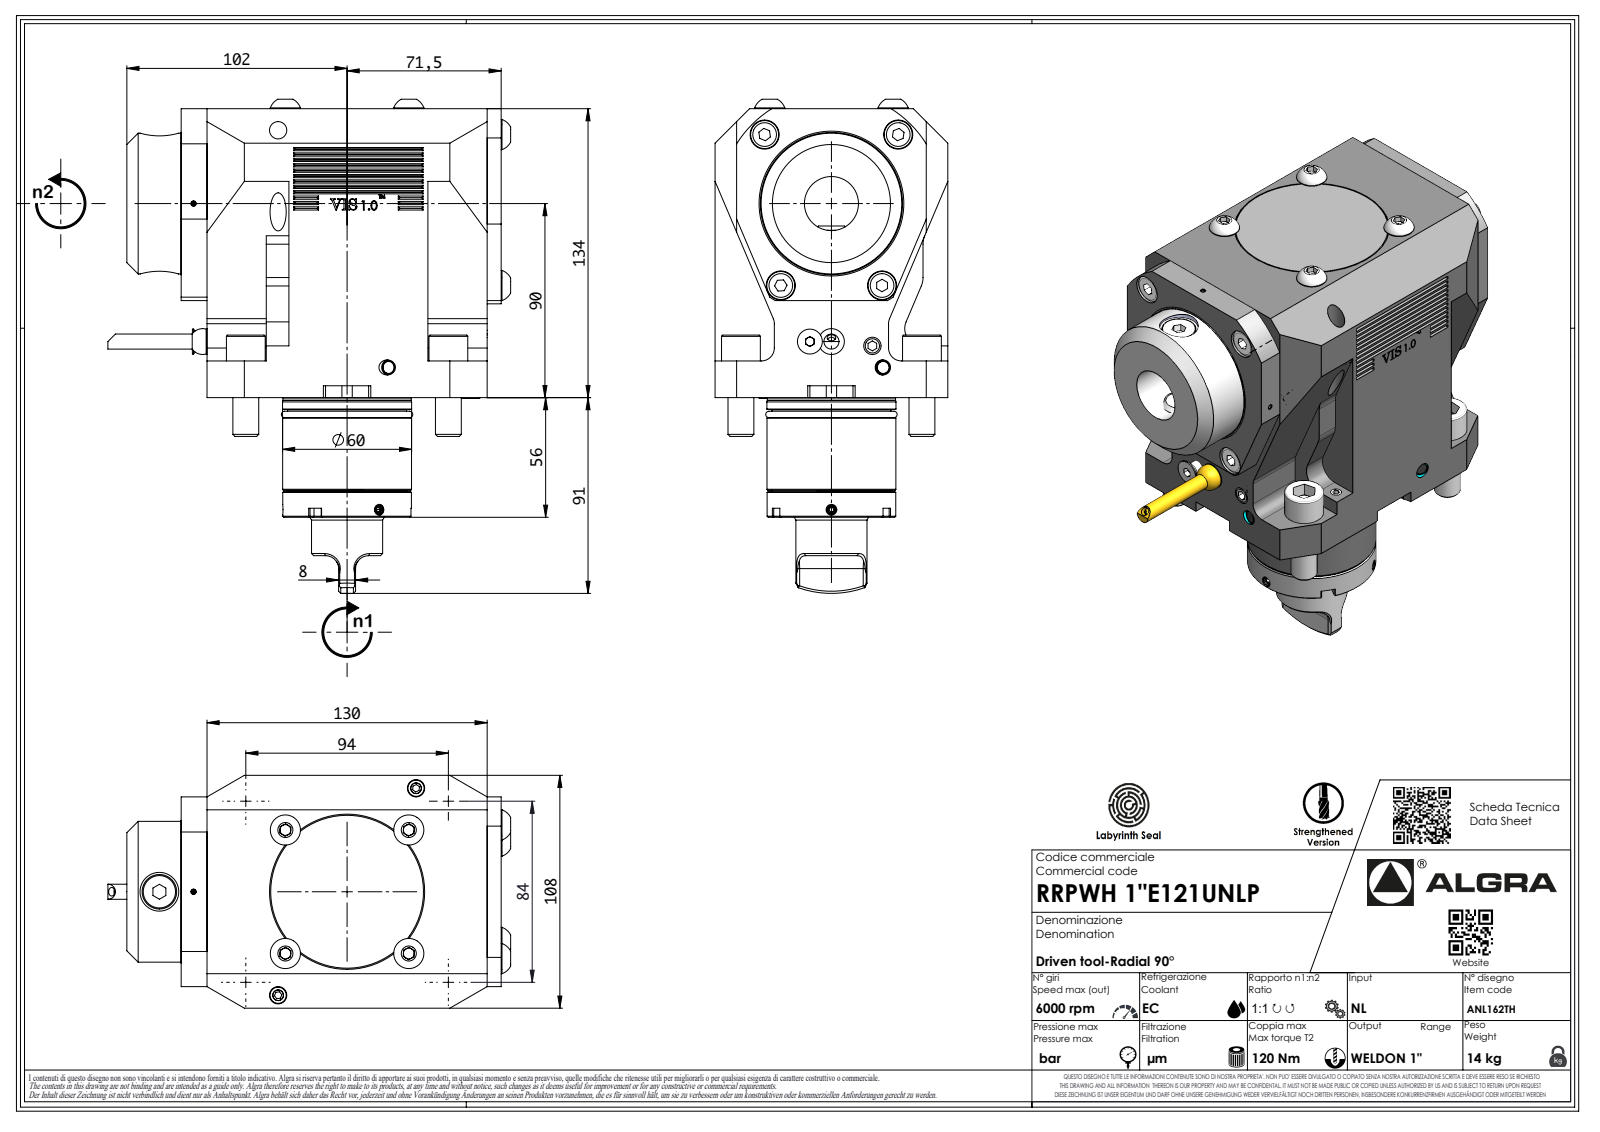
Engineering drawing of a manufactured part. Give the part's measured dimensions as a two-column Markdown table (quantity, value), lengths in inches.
| quantity | value |
| --- | --- |
| part name | RRPWH1E121UNLP |
| STEP written by | SolidWorks 2023 (AUTOMOTIVE_DESIGN) |
| units | inches |
| bodies | 1 solid, 921 faces (646 planar, 117 cylindrical, 158 other) |
| overall size | 8.85 × 7.185 × 4.252 |
| volume | 124.4 in³ |
| surface area | 200.6 in² |
| round holes (diameter × count) | 0.083 × 1, 0.157 × 1, 0.551 × 1, 0.709 × 1, 0.988 × 1 |
| round bosses / shafts (diameter × count) | 0.709 × 4, 0.472 × 4, 2.571 × 1, 2.358 × 1, 2.354 × 1, 2.35 × 1, 2.343 × 1, 2.173 × 1 |
| partial cylindrical surfaces (radius × count) | 0.008 × 21, 0.315 × 18, 0.236 × 10, 0.013 × 7, 0.02 × 7, 0.146 × 7, 0.394 × 4, 0.118 × 3 |
| main face-to-face distances | 5.276, 4.252, 1.083, 0.472, 5.846, 4.035, 0.256, 5.374, 0.217, 1.555 |
